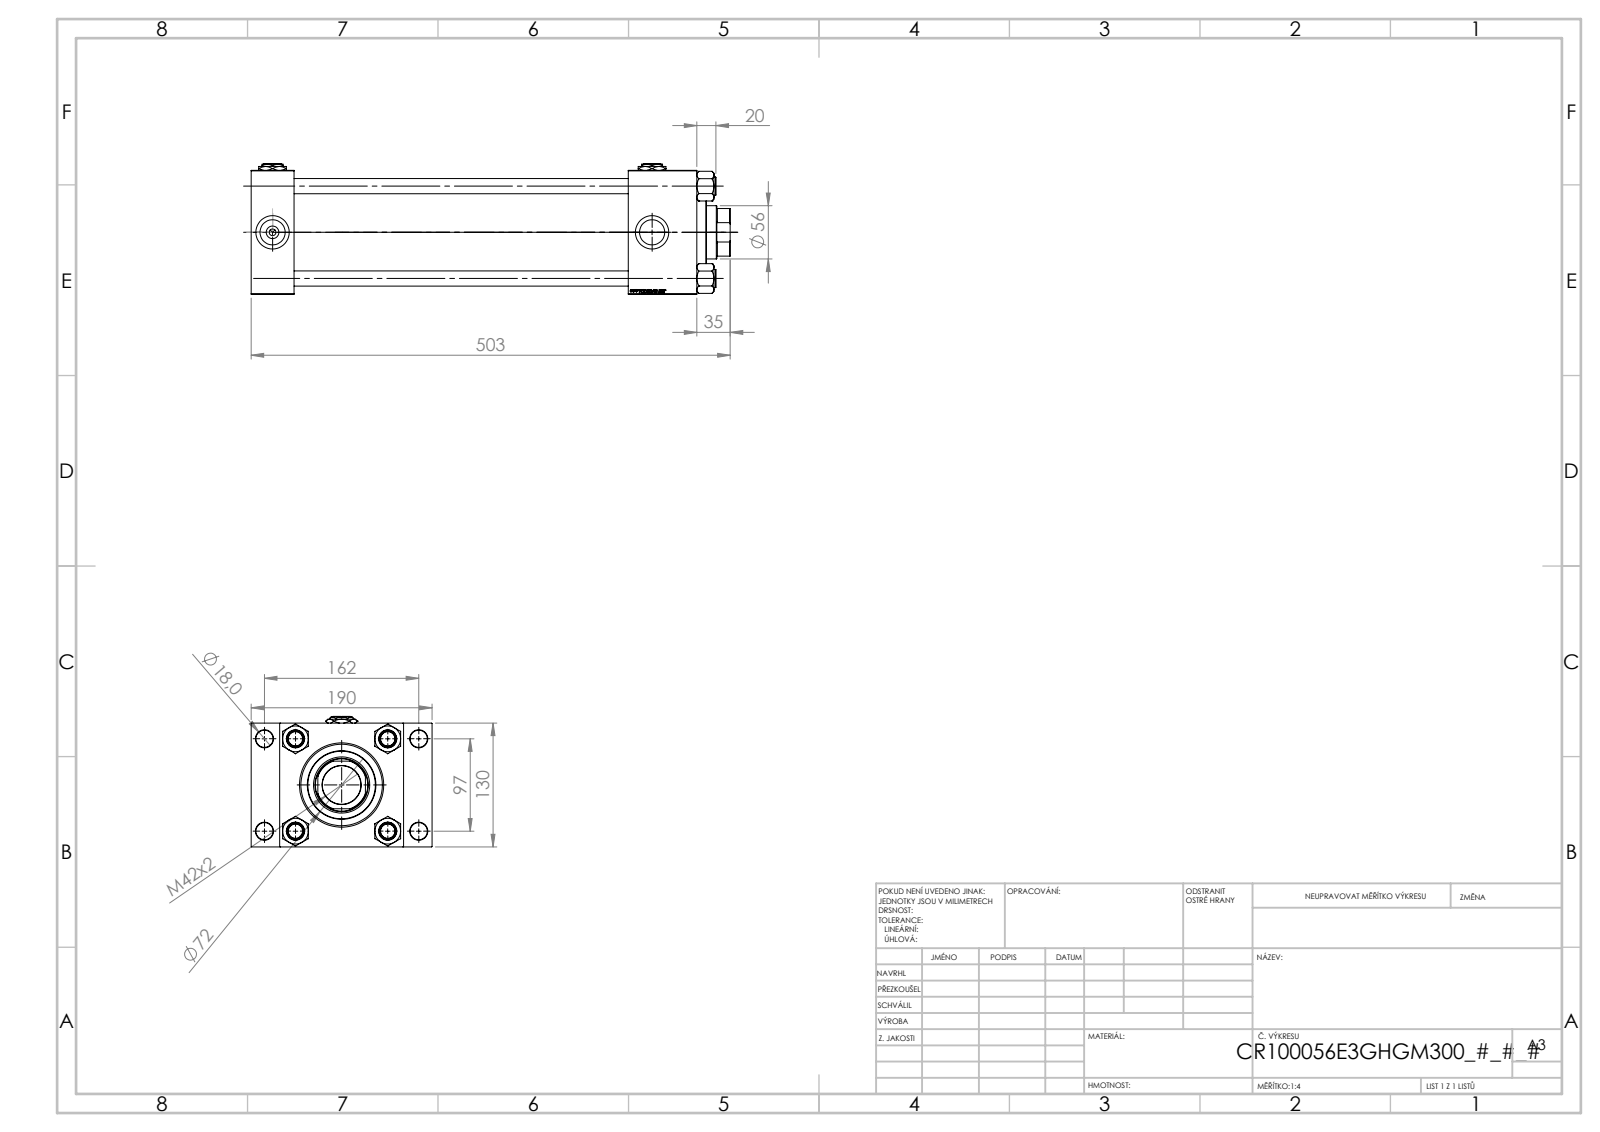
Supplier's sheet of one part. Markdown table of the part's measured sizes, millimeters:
| quantity | value |
| --- | --- |
| part name | NUT_M5_E; Zatka_pro_OIL_PORT; V215CR_TYCINKA_E; V215CR_VCP_E (+2 more) |
| STEP written by | SolidWorks 2019 (CONFIG_CONTROL_DESIGN) |
| units | millimeters |
| bodies | 13 solids, 1290 faces (595 planar, 101 cylindrical, 594 other) |
| overall size | 503 × 190 × 137 |
| volume | 3 967 000 mm³ |
| surface area | 671 136 mm² |
| round holes (diameter × count) | 16 × 4, 18 × 4, 26.44 × 4, 35 × 4, 7 × 3, 2.5 × 2, 40.5 × 1, 56 × 1, 59 × 1, 76 × 1, 85.5 × 1, 100 × 1 |
| round bosses / shafts (diameter × count) | 19 × 4, 106 × 1, 72 × 1 |
| partial cylindrical surfaces (radius × count) | 27 × 1 |
| main face-to-face distances | 130, 45, 468, 423, 30, 160, 396, 351, 72, 96 |
| hole center spacings | 32.55, 49.02, 62.87, 68.52, 94.41, 96.9, 101.73, 102.27 |
